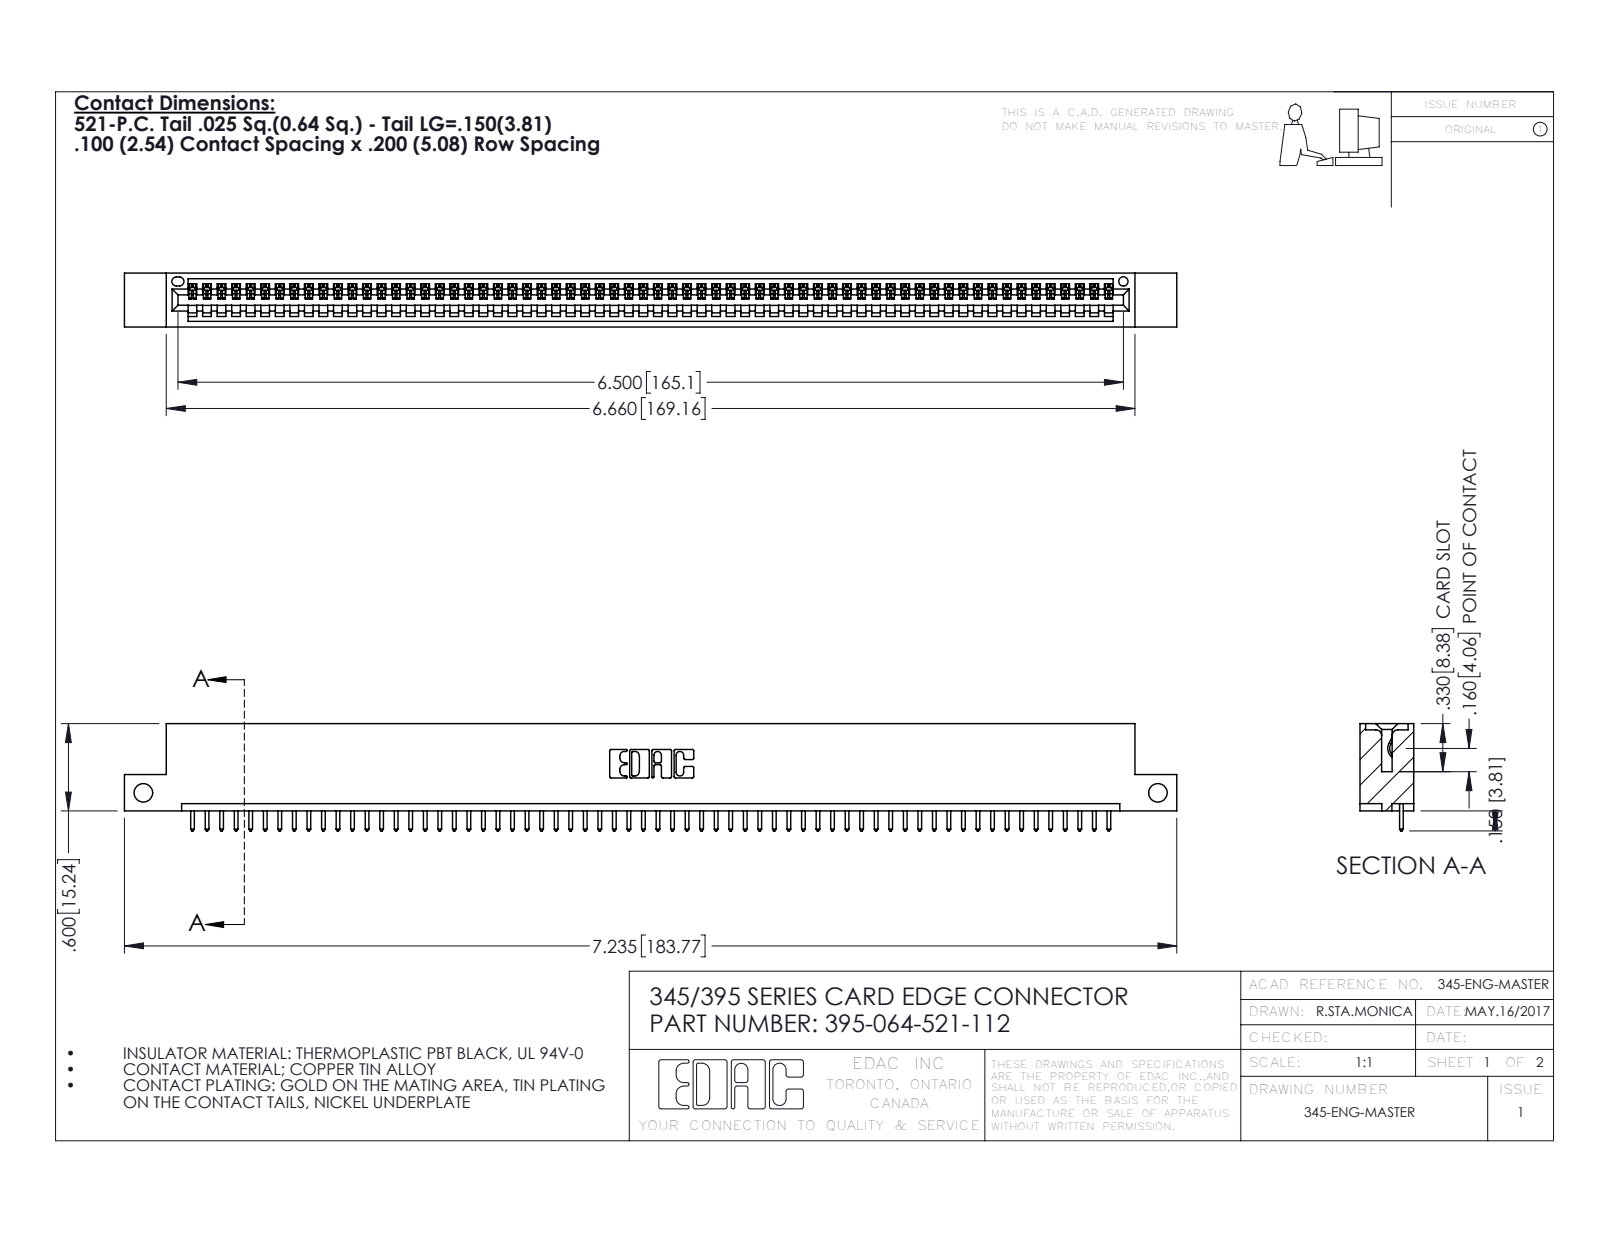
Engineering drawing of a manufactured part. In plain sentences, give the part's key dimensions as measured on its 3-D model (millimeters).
The part is named "395-064-521-112; 345 Part_Flush Mounting Lugs - Side Mount; 345-292-001_345-293-121". Its 3-D file was written by "SolidWorks 2016 (CONFIG_CONTROL_DESIGN)". It is 65 solids with 3838 faces: 2640 planar, 1198 cylindrical and 0 other. Overall it measures 183.8 by 18.7 by 9.4 millimeters. Its volume is 17 370 cubic millimeters and its surface area 22 520 square millimeters. Round holes: 2 of diameter 3.3, 1 of diameter 1.6. Partial cylindrical surfaces (rounded edges, fillets, slot ends): 128 of radius 0.2, 128 of radius 0.3, 22 of radius 0.3, 6 of radius 0.2, 6 of radius 0.8, 3 of radius 0.7, 2 of radius 0.8, 2 of radius 1. The main face-to-face distances are 7.6, 1.8, 9.4, 5.1, 2.5, 6.9, 0.6, 5.7, 3.8, 1.8. The hole center spacings are 177.2.
